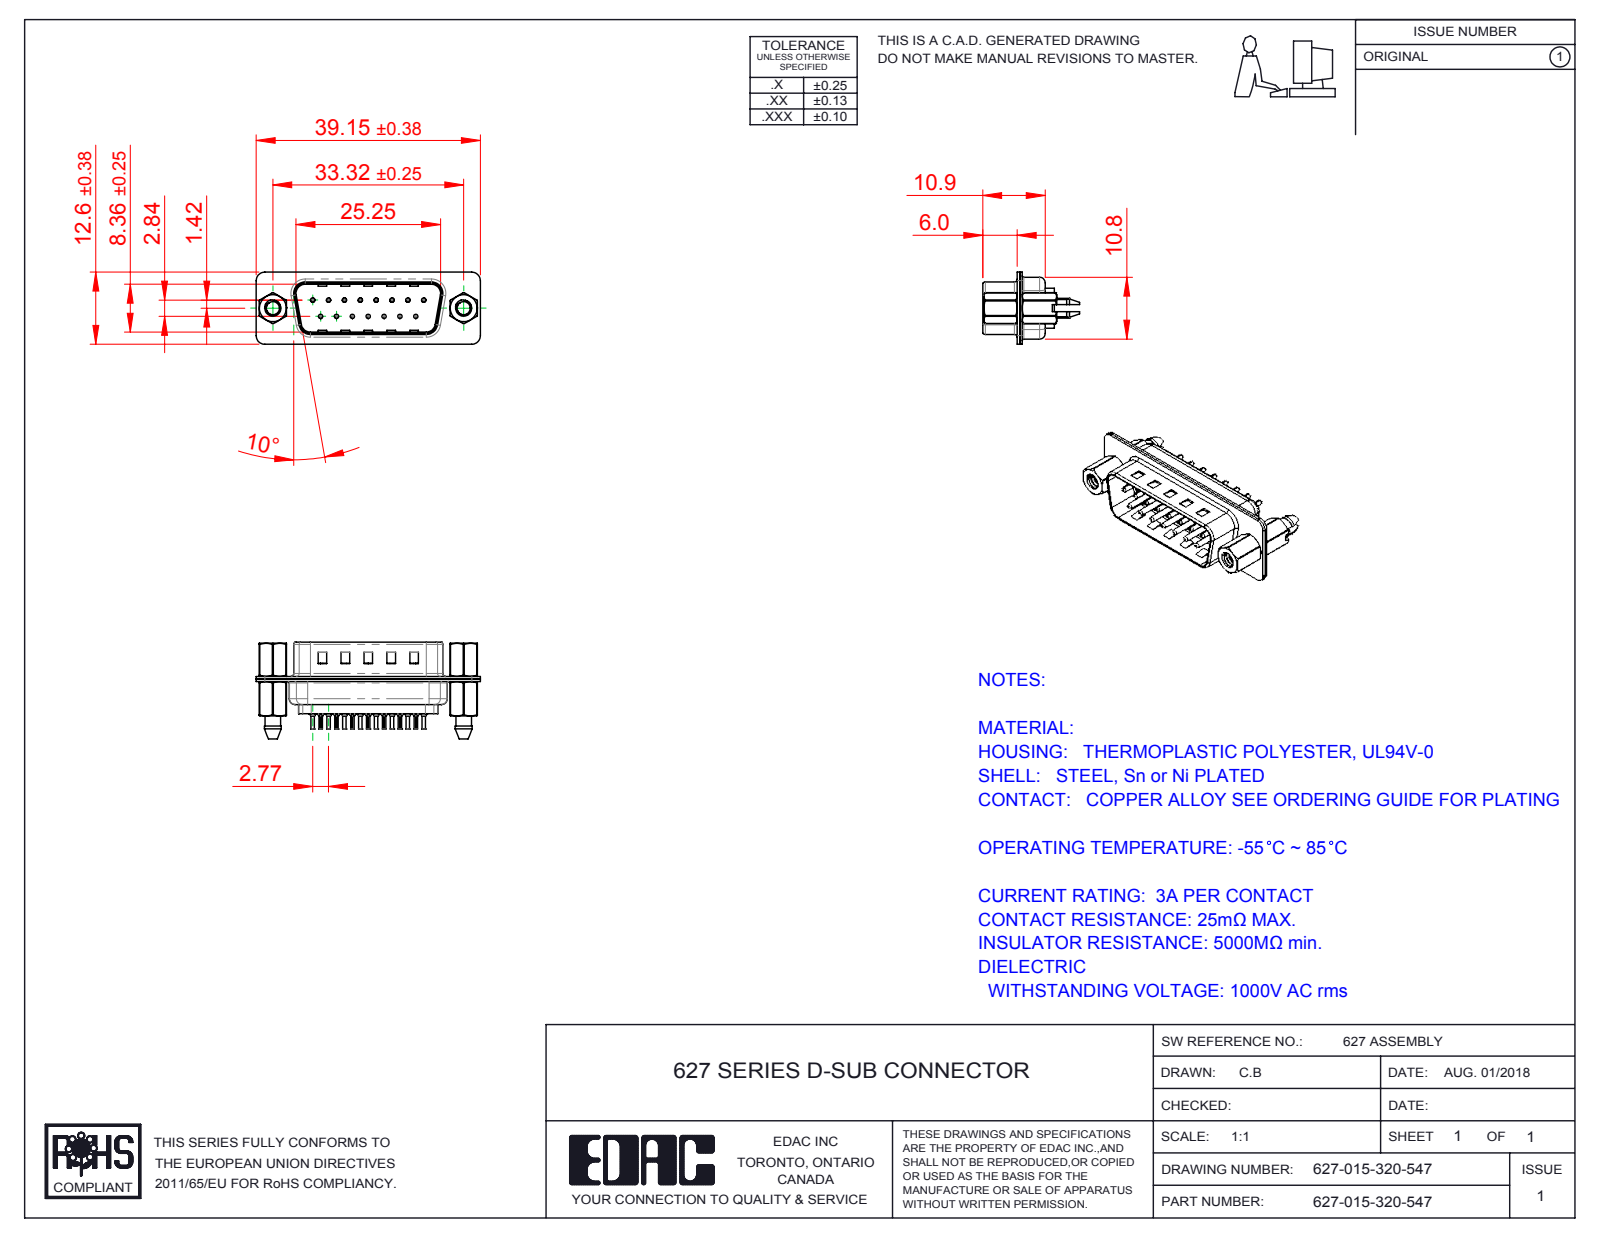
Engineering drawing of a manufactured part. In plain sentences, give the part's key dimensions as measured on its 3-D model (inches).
The part is named "627 Contact Row 1_20L; 627 Shell Rear_15 Contacts; 627 Shell Front_15 Contacts; 627 Housing_15 LP (+4 more)". Its 3-D file was written by "SolidWorks 2016 (CONFIG_CONTROL_DESIGN)". It is 22 solids with 2010 faces: 553 planar, 792 cylindrical and 665 other. Overall it measures 1.541 by 0.665 by 0.496 inches. Its volume is 0.131 cubic inches and its surface area 9.418 square inches. Round holes: 15 of diameter 0.008, 15 of diameter 0.014, 15 of diameter 0.043, 15 of diameter 0.063, 2 of diameter 0.089, 2 of diameter 0.09, 2 of diameter 0.157, 2 of diameter 0.189. Round bosses or shafts: 15 of diameter 0.079, 15 of diameter 0.059, 15 of diameter 0.03, 15 of diameter 0.024, 2 of diameter 0.193, 2 of diameter 0.11. Partial cylindrical surfaces (rounded edges, fillets, slot ends): 30 of radius 0.004, 18 of radius 0.059, 12 of radius 0.079, 10 of radius 0.063, 8 of radius 0.02, 4 of radius 0.01, 4 of radius 0.024, 4 of radius 0.026. The main face-to-face distances are 0.016, 0.018, 0.035, 0.032, 0.377, 0.345, 0.187, 0.059, 0.055, 0.256. The hole center spacings are 0.124, 0.109, 0.218, 0.327, 0.436, 0.198, 0.198, 0.294.
